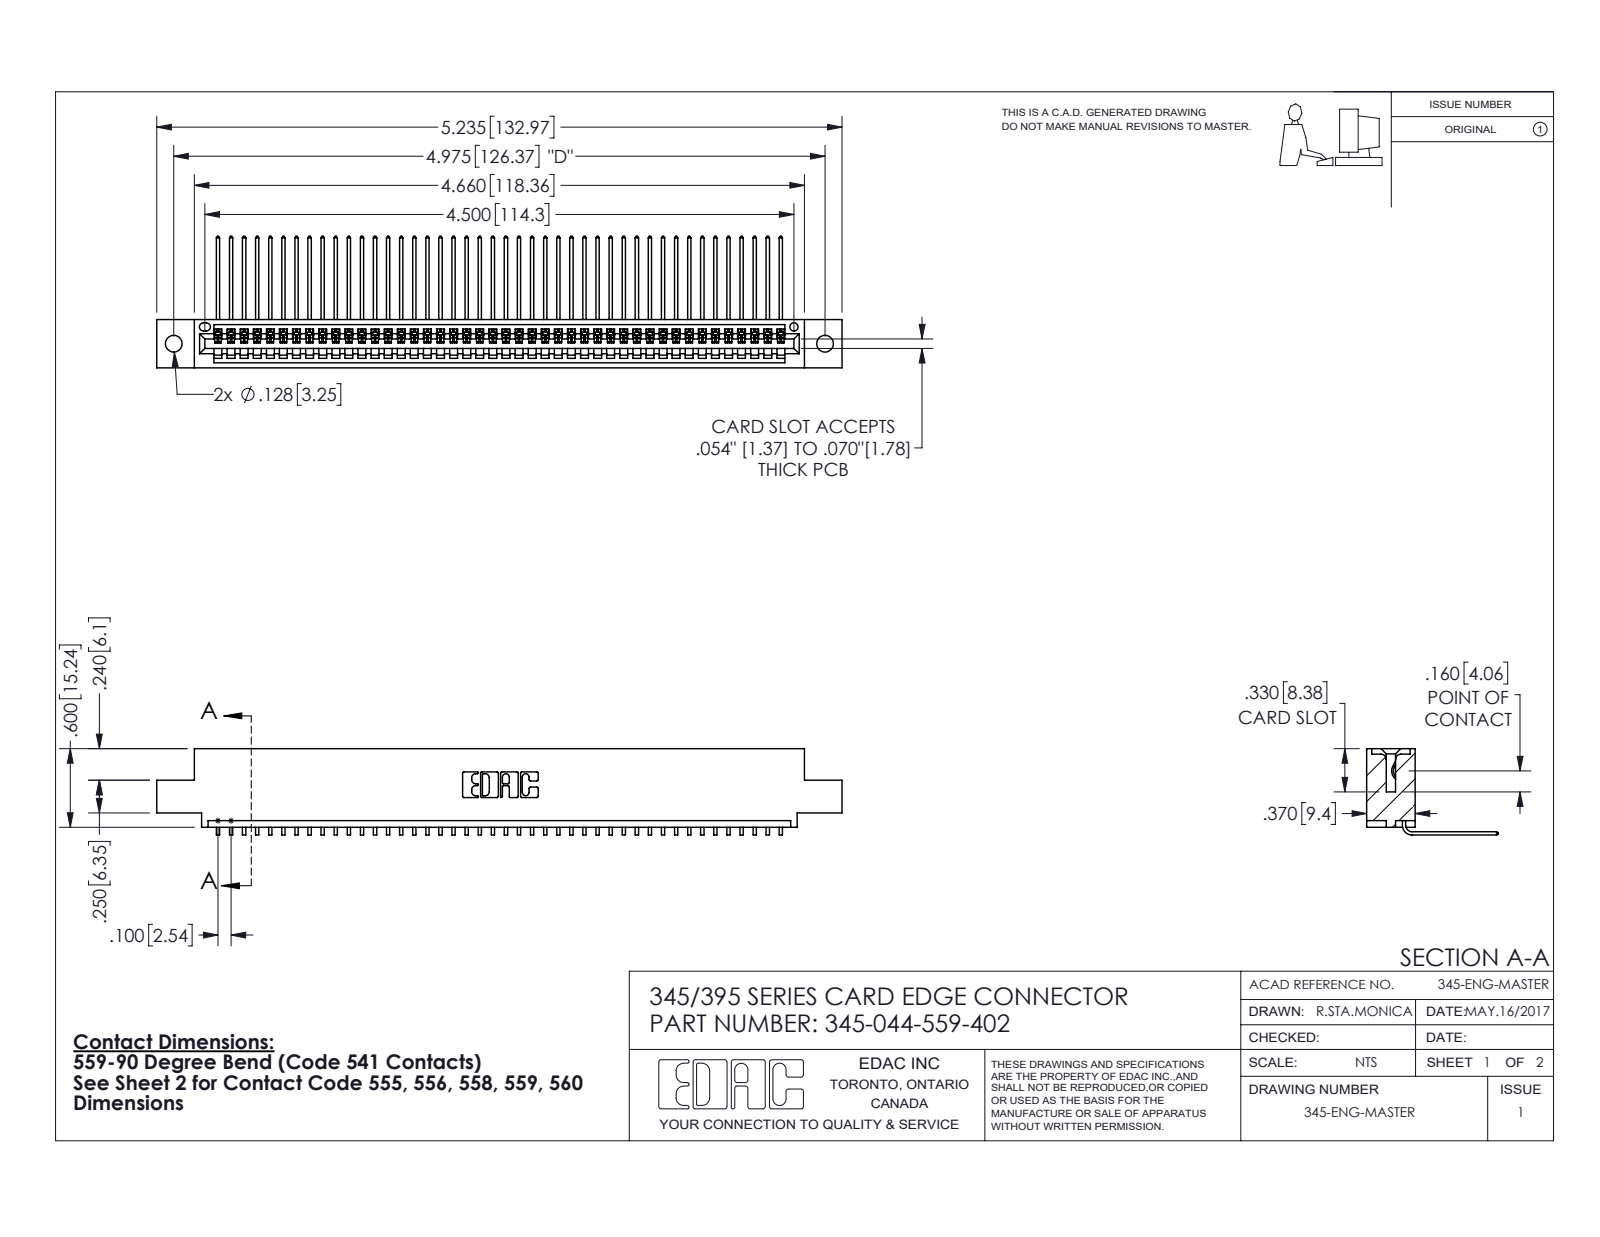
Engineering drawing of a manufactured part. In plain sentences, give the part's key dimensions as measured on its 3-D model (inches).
The part is named "345 Part_0.110 Offset - 0.128 Dia; 345-292-001_558 559 Tail - 1; 345-044-559-402". Its 3-D file was written by "SolidWorks 2016 (CONFIG_CONTROL_DESIGN)". It is 45 solids with 2770 faces: 1932 planar, 838 cylindrical and 0 other. Overall it measures 5.235 by 1.005 by 0.659 inches. Its volume is 0.774 cubic inches and its surface area 27.21 square inches. Round holes: 2 of diameter 0.128, 1 of diameter 0.064. Partial cylindrical surfaces (rounded edges, fillets, slot ends): 88 of radius 0.006, 22 of radius 0.01, 6 of radius 0.007, 6 of radius 0.031, 3 of radius 0.026, 2 of radius 0.031, 2 of radius 0.04, 1 of radius 0.014. The main face-to-face distances are 0.072, 0.298, 0.37, 0.2, 0.098, 0.272, 0.025, 0.225, 0.149, 0.072. The hole center spacings are 0.27, 4.739, 4.975.
